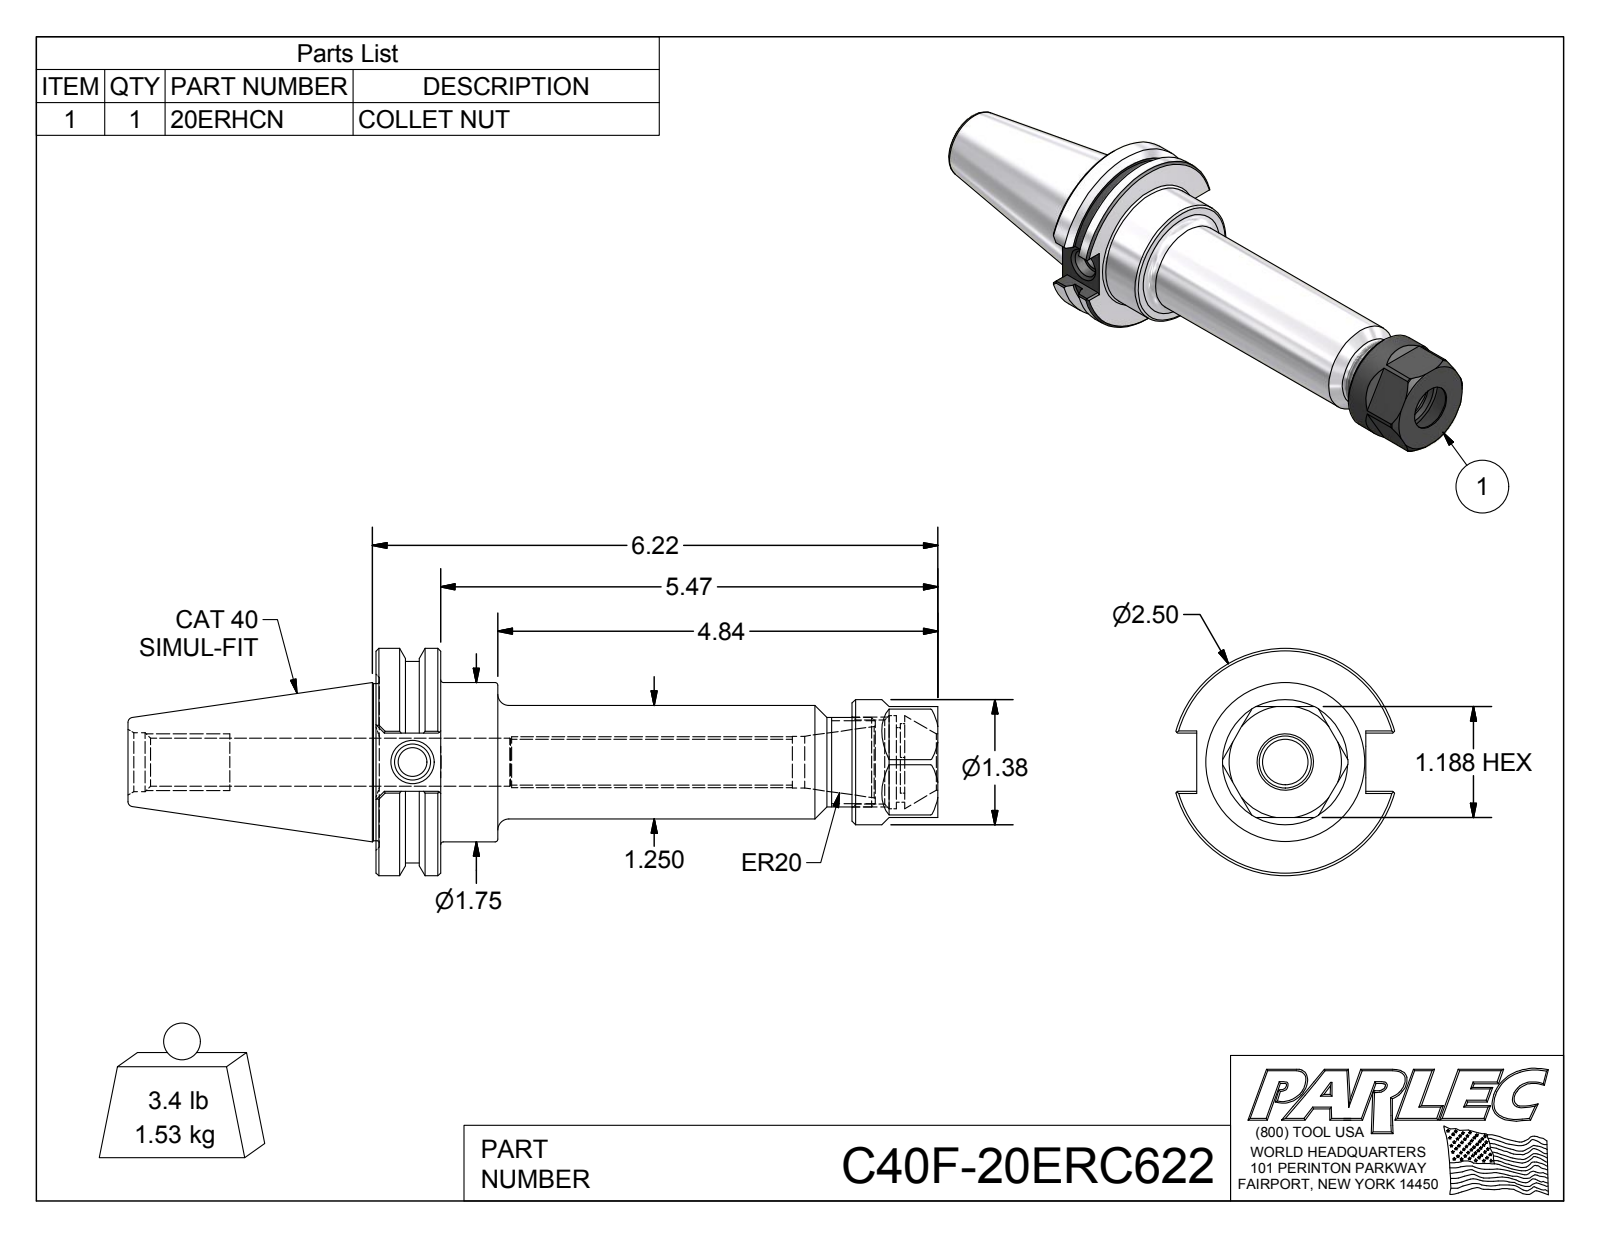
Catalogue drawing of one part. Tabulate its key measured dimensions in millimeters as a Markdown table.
| quantity | value |
| --- | --- |
| part name | C40F-20ERC622; C40F-20ER6-1; 20ERHCN |
| STEP written by | Autodesk Inventor 2012 (AUTOMOTIVE_DESIGN) |
| units | millimeters |
| bodies | 2 solids, 118 faces (51 planar, 22 cylindrical, 45 other) |
| overall size | 226.3 × 63.5 × 61.1 |
| volume | 200 200 mm³ |
| surface area | 43 480 mm² |
| round holes (diameter × count) | 8 × 1, 10.1 × 1, 12.8 × 1, 13.4 × 1, 14.5 × 1, 15.7 × 1, 16.5 × 1, 20.8 × 1, 23.5 × 1, 26 × 1 |
| round bosses / shafts (diameter × count) | 63.5 × 1, 56.3 × 1, 44.5 × 1, 43.9 × 1, 35 × 1, 31.8 × 1, 25 × 1 |
| partial cylindrical surfaces (radius × count) | 10.7 × 1 |
| main face-to-face distances | 18, 31, 157, 138.9, 133, 114.9, 24, 7.4, 23.6, 34 |
| hole center spacings | 0.9 |
